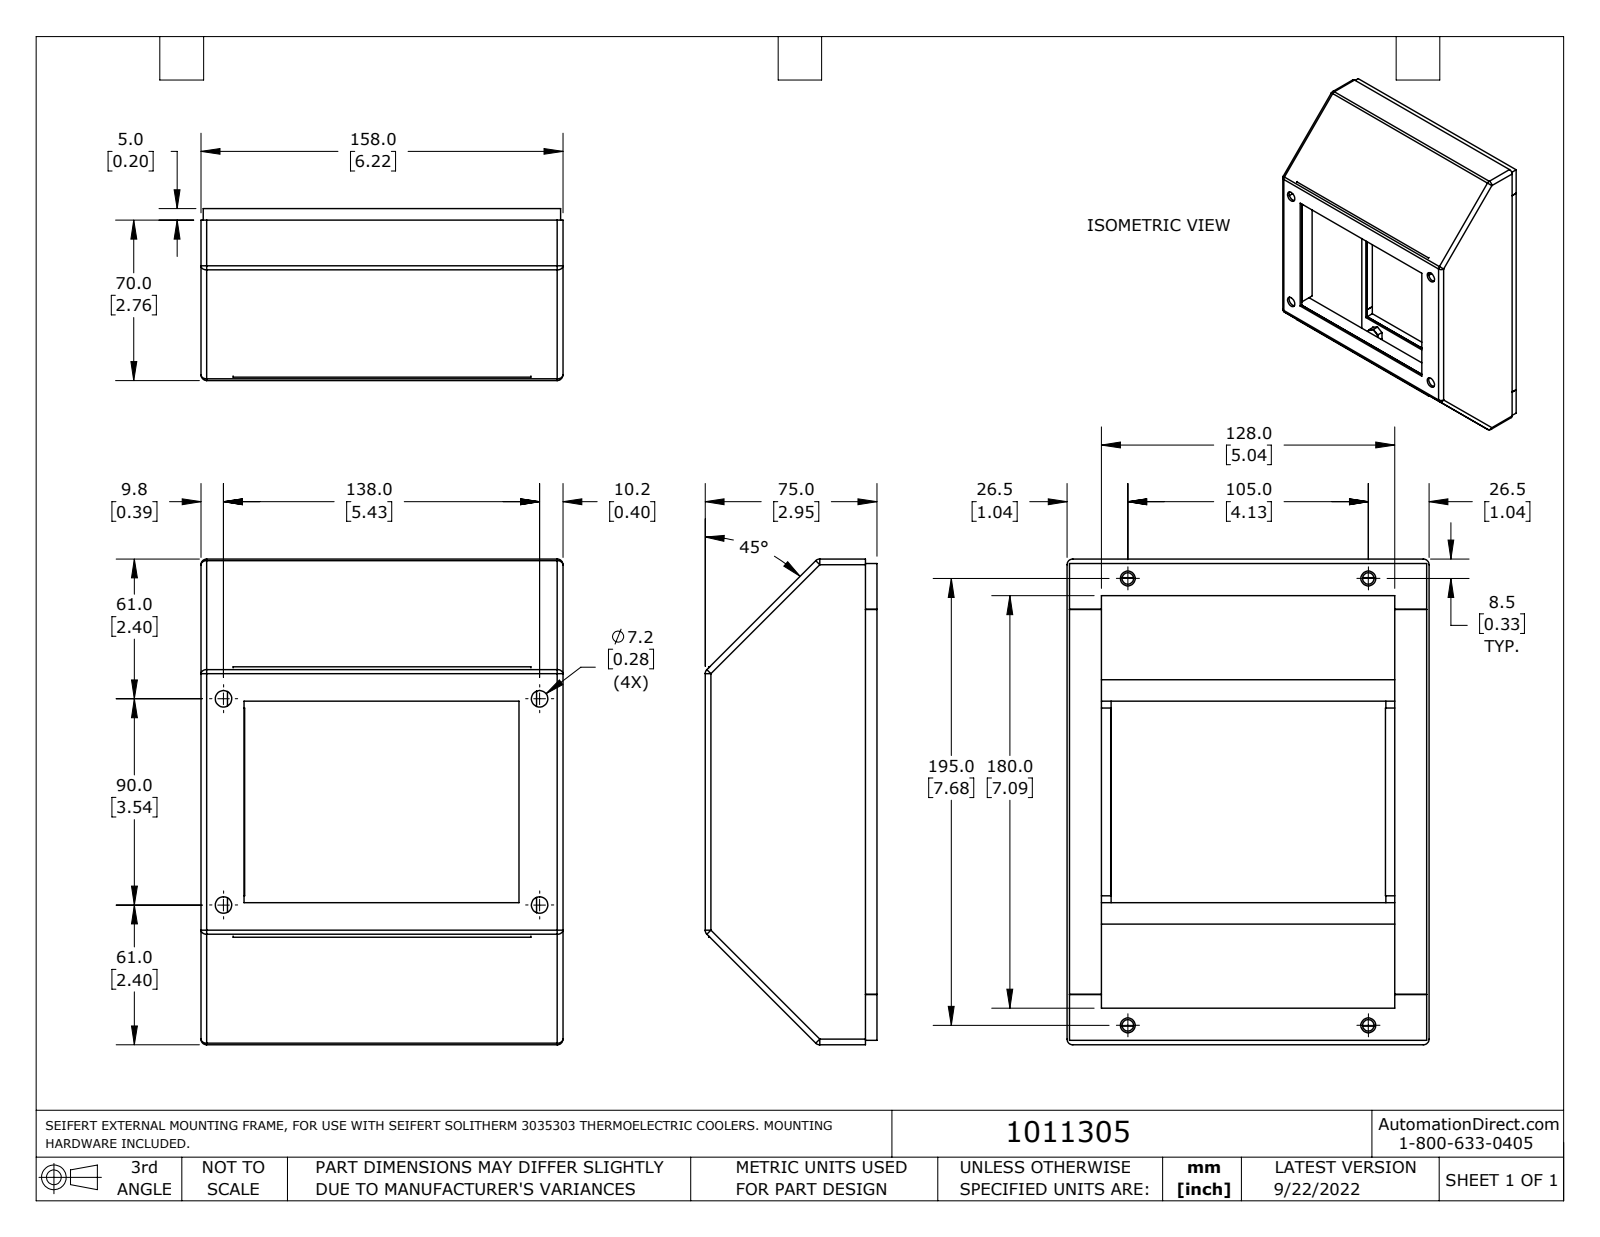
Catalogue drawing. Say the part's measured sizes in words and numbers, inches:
The part is named "1011305". Its 3-D file was written by "SolidWorks 2021 (AUTOMOTIVE_DESIGN)". It is 17 solids with 338 faces: 264 planar, 50 cylindrical and 24 other. Overall it measures 8.346 by 6.22 by 2.953 inches. Its volume is 35.78 cubic inches and its surface area 436.9 square inches. Round holes: 4 of diameter 0.197, 4 of diameter 0.256, 4 of diameter 0.283. Round bosses or shafts: 4 of diameter 0.402, 4 of diameter 0.35. Partial cylindrical surfaces (rounded edges, fillets, slot ends): 16 of radius 0.039, 14 of radius 0.098. The main face-to-face distances are 0.059, 0.394, 0.453, 5.768, 6.161, 5.709, 6.102, 2.697, 5.315, 6.22. The hole center spacings are 2.165, 2.169, 3.543, 4.134, 5.204, 5.218, 5.433, 5.647.
